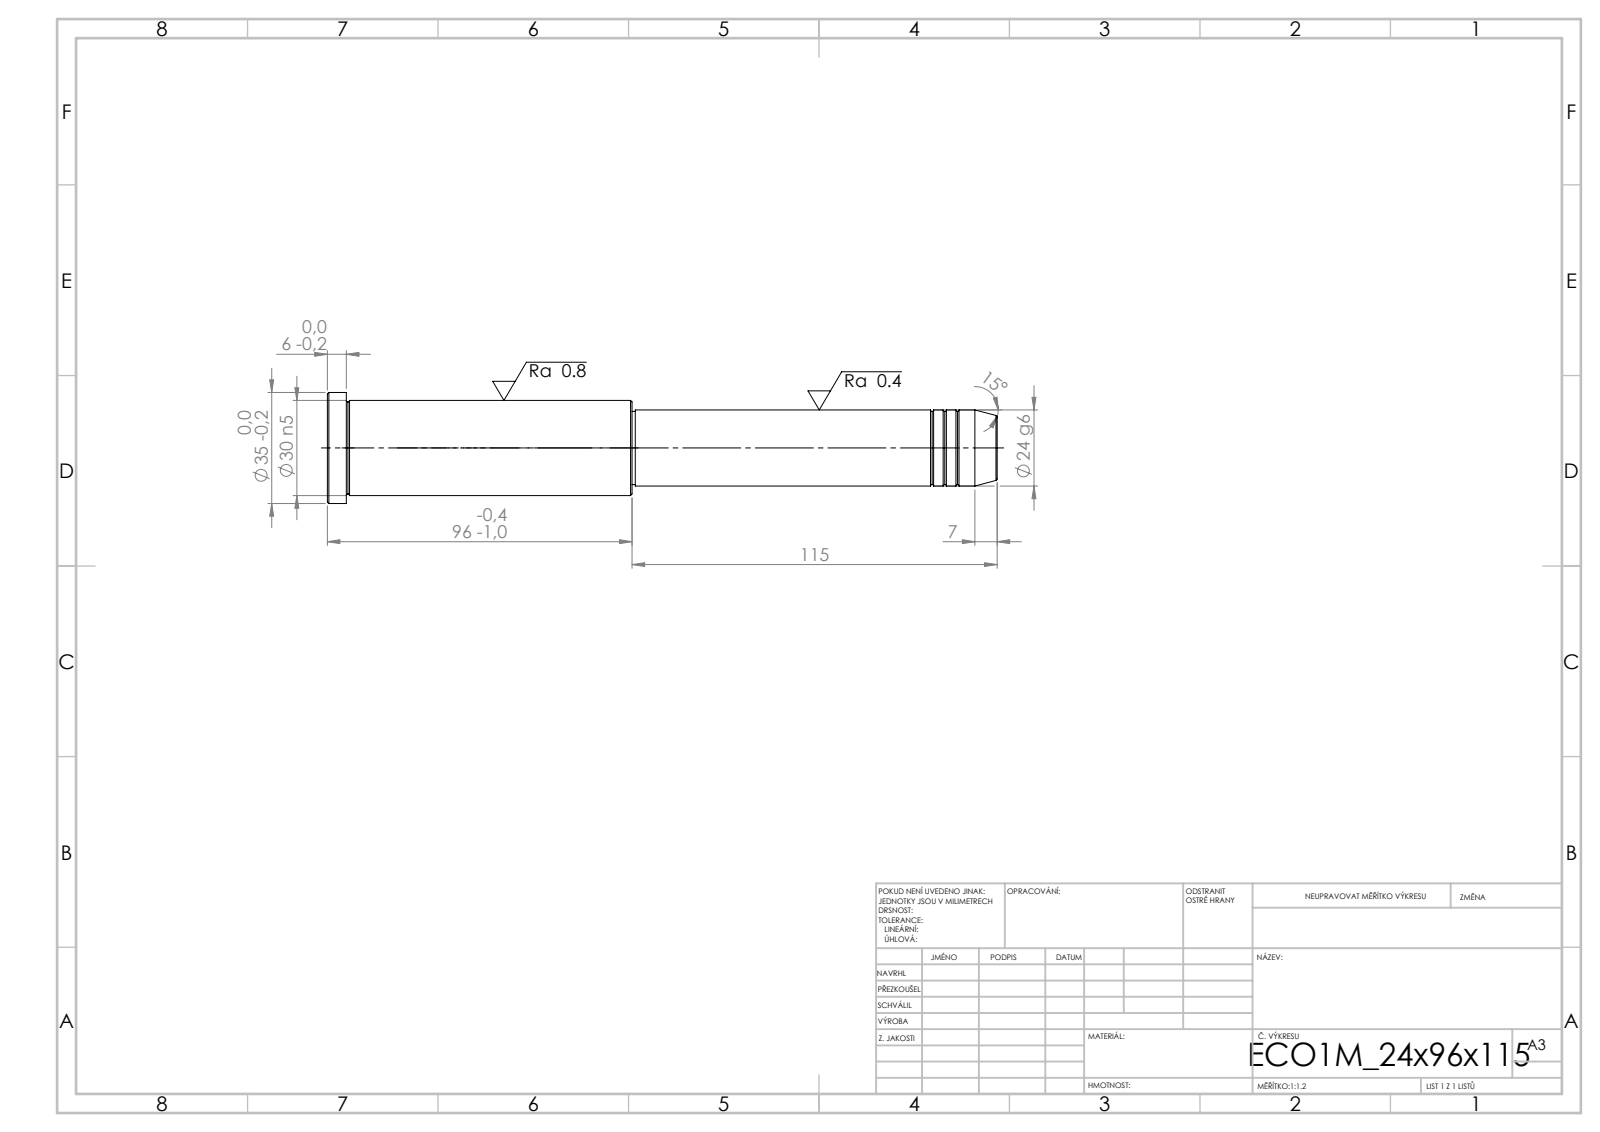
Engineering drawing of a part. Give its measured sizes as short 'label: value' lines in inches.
written by: SolidWorks 2019 (CONFIG_CONTROL_DESIGN)
unit: in
bodies: 1 solid, 43 faces (5 planar, 14 cylindrical, 24 other)
size: 8.307 × 1.378 × 1.378
volume: 7.369 in³; area: 30.62 in²
bosses: 1× ⌀1.378, 1× ⌀1.181, 1× ⌀0.945, 1× ⌀0.906
face distances: 8.307, 8.071, 0.236, 4.528, 3.543, 3.78, 4.488, 0.039, 3.583, 3.819
